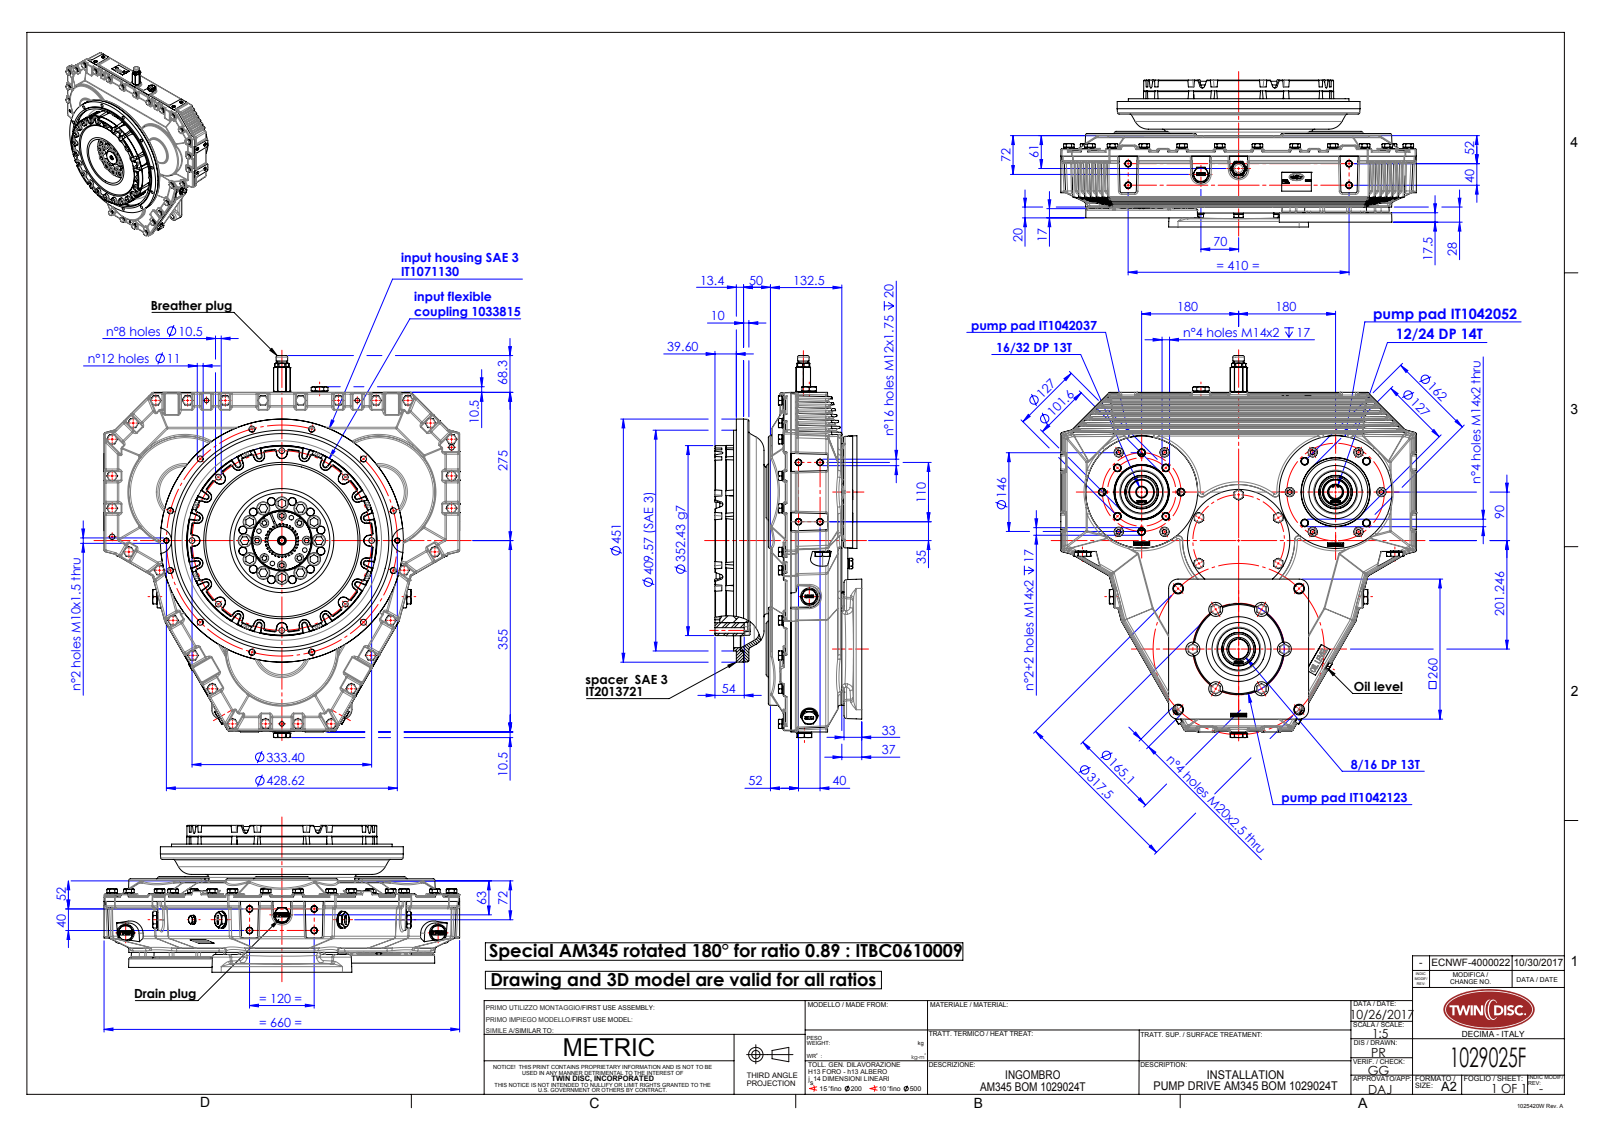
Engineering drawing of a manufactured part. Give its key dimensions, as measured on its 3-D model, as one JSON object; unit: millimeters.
{"part_name": "IT1042037-installation; IT1071130-installation; ITBC0610000_rev00-installation; IT2013721 (+8 more)", "step_written_by": "SolidWorks 2015 (AUTOMOTIVE_DESIGN)", "units": "millimeters", "bodies": {"solids": 169, "faces": 9502, "planar": 4038, "cylindrical": 2556, "other": 2908}, "overall_size": [708.8, 660, 272.5], "volume_mm3": 41870000, "surface_area_mm2": 4347000, "round_holes": [[10.2, 54], [8.5, 49], [11, 46], [10.5, 38], [14, 36], [12, 26], [17, 23], [10, 11], [10.92, 8], [13, 7], [12.2, 6], [26, 6]], "round_bosses_or_shafts": [[10, 61], [16.2, 41], [18.1, 35], [16, 30], [24, 12], [21.1, 6], [18, 6], [12, 6]], "partial_cylinders_radius": [[3, 344], [2, 126], [5, 114], [2.54, 72], [0.45, 58], [1.54, 48], [9.4, 24], [10, 24]], "face_to_face_distances": [21, 152.5, 94.5, 20, 4, 115.5, 37, 17, 42, 8], "hole_center_spacings": [120, 57.4, 75, 138.58, 40, 207.84, 51.37, 66.61]}
